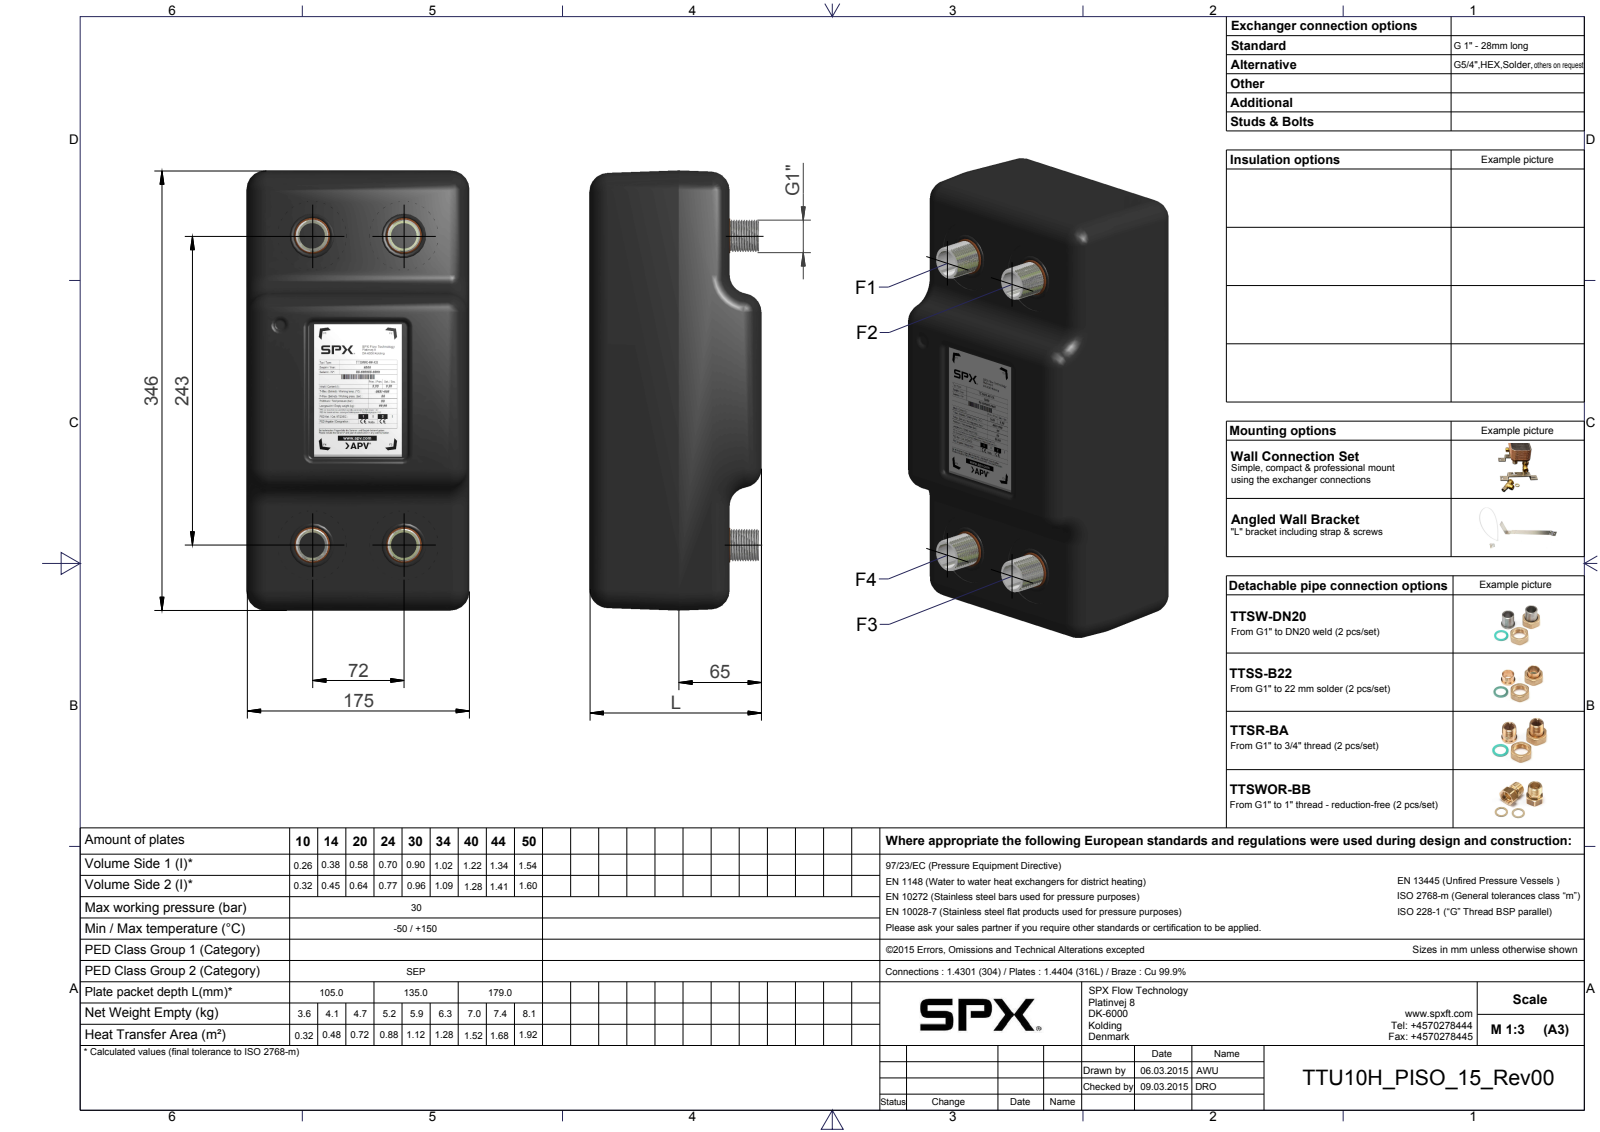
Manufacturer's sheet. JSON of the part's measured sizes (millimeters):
{"part_name": "PBUX10", "step_written_by": "Autodesk Inventor 2015 (CONFIG_CONTROL_DESIGN)", "units": "millimeters", "bodies": {"solids": 2, "faces": 274, "planar": 72, "cylindrical": 104, "other": 98}, "overall_size": [346, 175, 135], "volume_mm3": 6960000, "surface_area_mm2": 277968, "round_holes": [[20, 4], [25.6, 4], [28, 4], [32, 4], [54.4, 4]], "partial_cylinders_radius": [[15, 23], [2, 18], [4, 16], [5, 4], [25, 4]], "face_to_face_distances": [174.83, 1, 110, 23, 132, 22, 3, 28, 25, 5], "hole_center_spacings": [72, 243, 253.44]}
